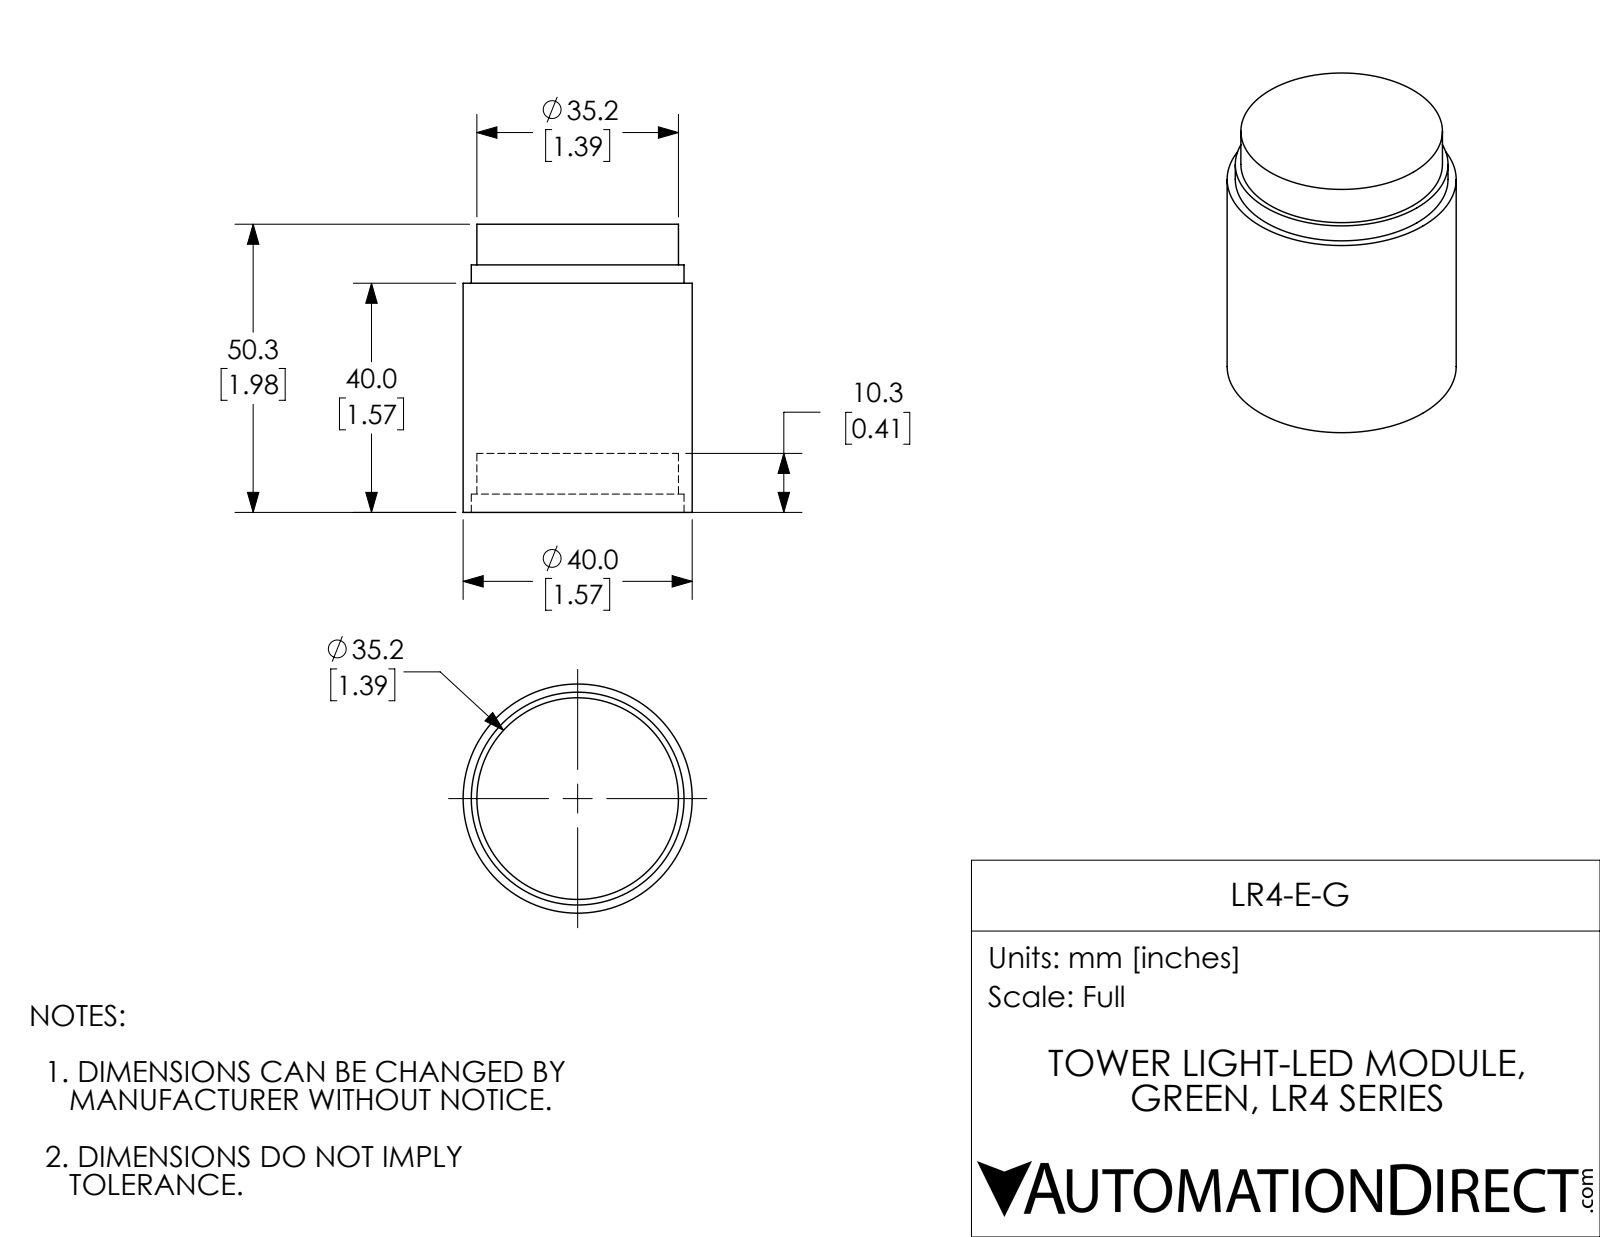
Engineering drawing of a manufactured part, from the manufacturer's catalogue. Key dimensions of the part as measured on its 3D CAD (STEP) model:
Part name (STEP PRODUCT): LR4-E-G
STEP written by: SolidWorks 2017 (AUTOMOTIVE_DESIGN)
Units: inches
Bodies: 1 solid, 16 faces (6 planar, 10 cylindrical, 0 other)
Overall size (bounding box): 1.98 × 1.575 × 1.575
Volume: 3.067 in³ · Surface area: 15.28 in²
Round holes (diameter × count): ⌀1.386 ×1, ⌀1.463 ×1
Round bosses / shafts (diameter × count): ⌀1.575 ×1
Main face-to-face distances: 1.575, 0.406, 0.126, 0.28, 1.98, 1.169, 1.701, 1.295, 1.449, 1.854
